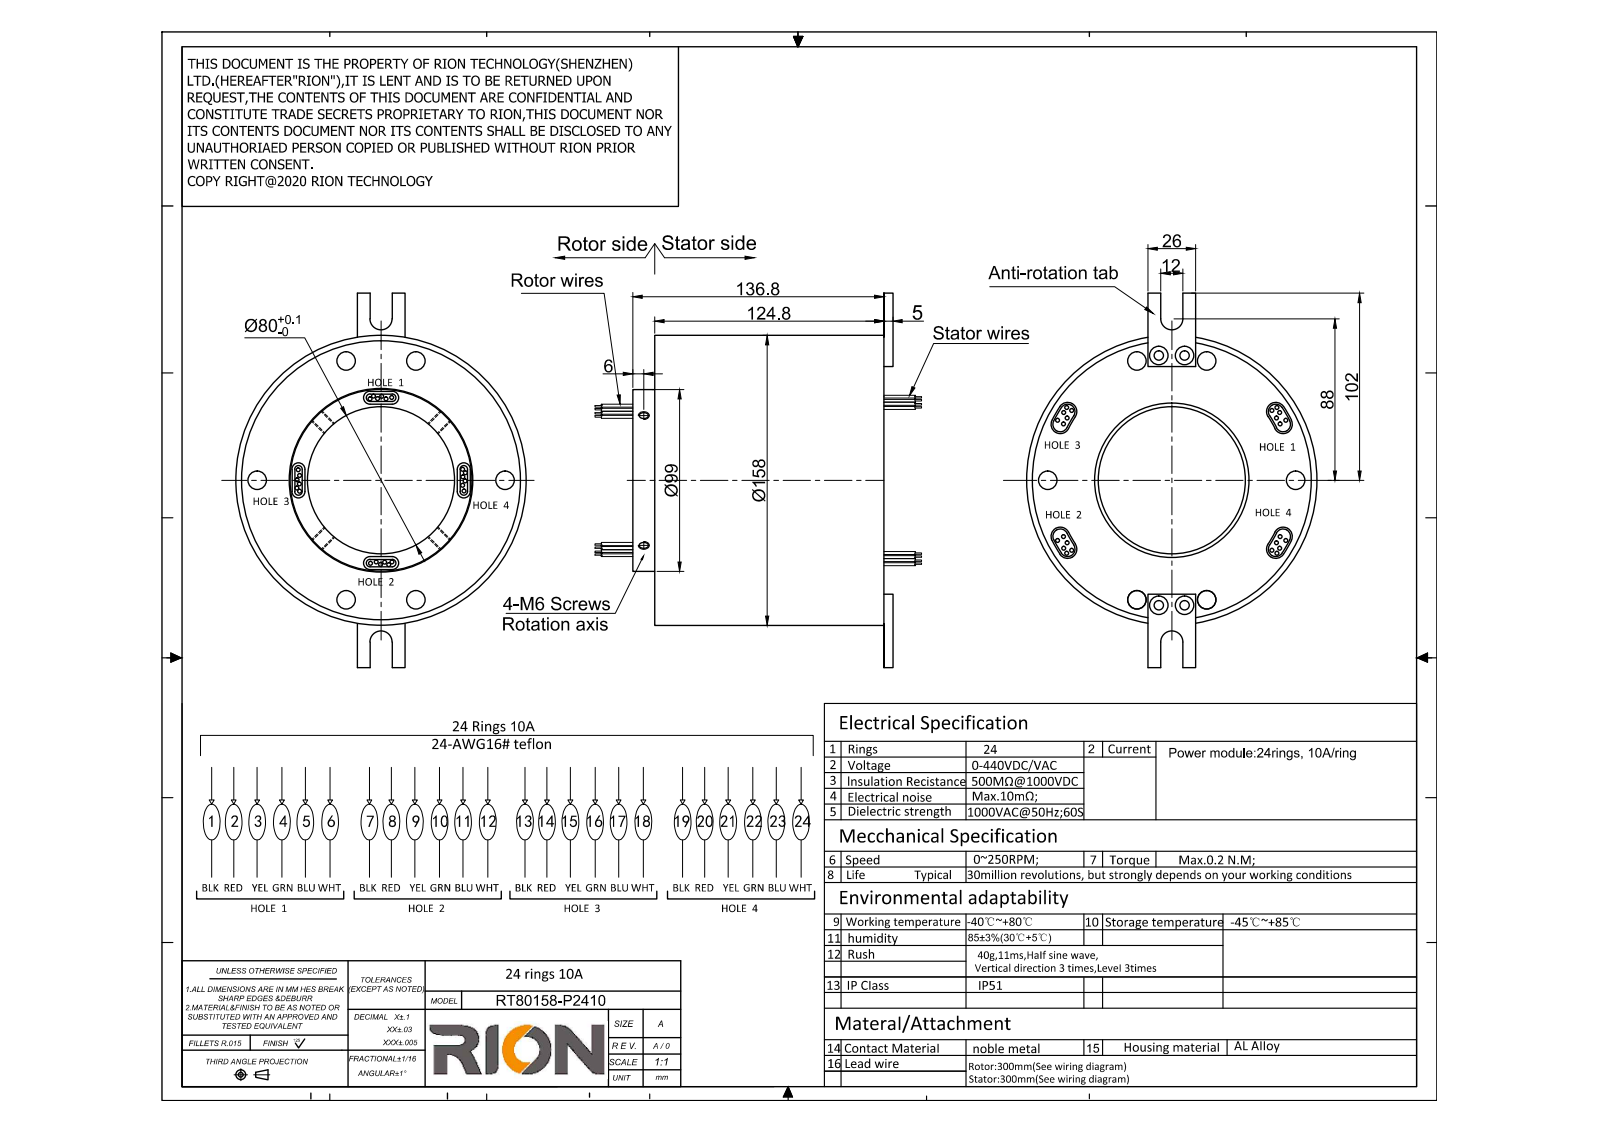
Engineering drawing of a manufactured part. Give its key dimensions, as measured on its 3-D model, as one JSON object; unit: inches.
{"part_name": "MT80158-P2410", "step_written_by": "SolidWorks 2014 (CONFIG_CONTROL_DESIGN)", "units": "inches", "bodies": {"solids": 1, "faces": 284, "planar": 106, "cylindrical": 162, "other": 16}, "overall_size": [8.063, 8.031, 6.22], "volume_in3": 113.7, "surface_area_in2": 237, "round_holes": [[0.197, 8], [0.165, 4], [3.15, 1], [3.701, 1], [5.984, 1]], "round_bosses_or_shafts": [[0.083, 48], [6.22, 1], [5.976, 1], [3.898, 1], [3.693, 1]], "partial_cylinders_radius": [[0.079, 8], [0.157, 8], [0.236, 2]], "face_to_face_distances": [4.913, 0.472, 5.386, 0.197, 5.583, 5.11, 0.039, 5.346, 1.024, 4.874], "hole_center_spacings": [2.691, 0.551, 5.354, 5.383]}
